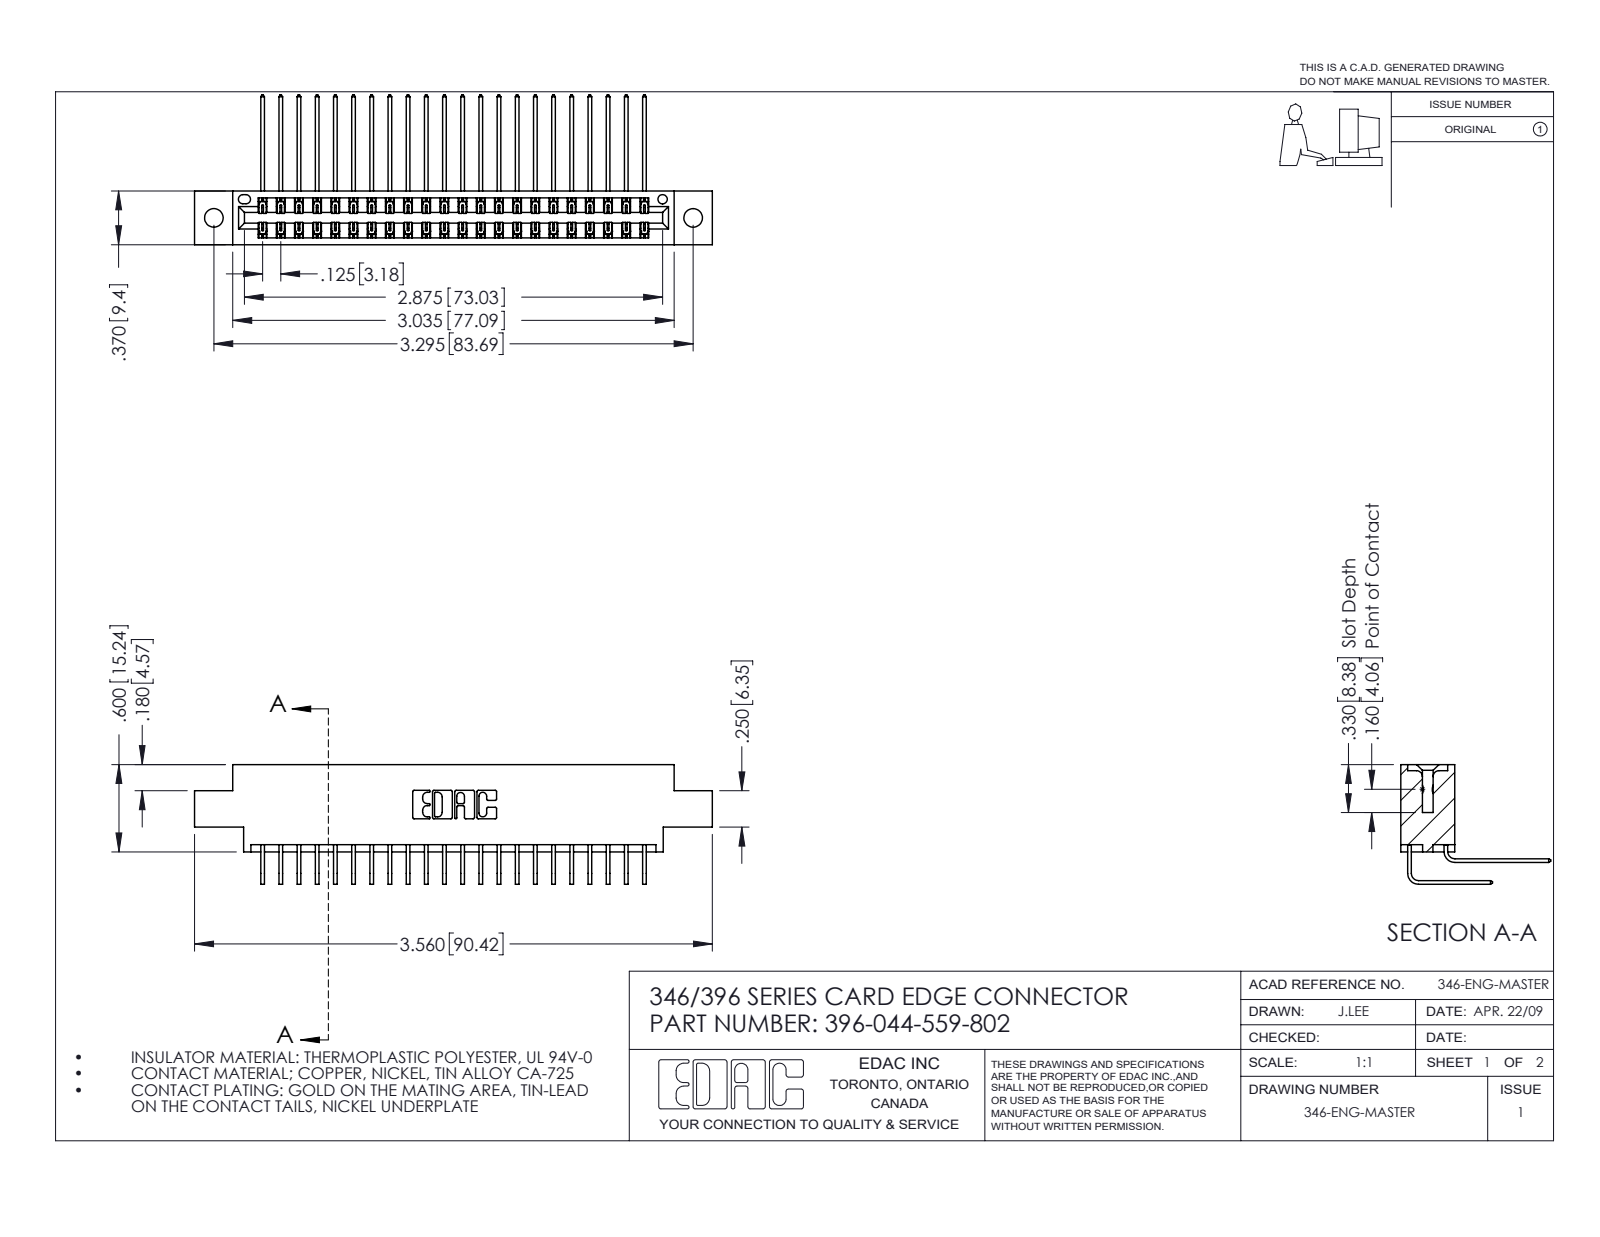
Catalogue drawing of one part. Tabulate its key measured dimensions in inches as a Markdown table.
| quantity | value |
| --- | --- |
| part name | 345-292-001_559 Tail - 2; 346 Part_0.170 Offset - 0.128 Dia; 345-292-001_558 559 Tail - 1; 396-044-559-802 |
| STEP written by | SolidWorks 2016 (CONFIG_CONTROL_DESIGN) |
| units | inches |
| bodies | 45 solids, 2502 faces (1708 planar, 794 cylindrical, 0 other) |
| overall size | 3.56 × 1.03 × 0.823 |
| volume | 0.532 in³ |
| surface area | 19.85 in² |
| round holes (diameter × count) | 0.128 × 2, 0.064 × 1 |
| partial cylindrical surfaces (radius × count) | 0.006 × 66, 0.01 × 22, 0.007 × 6, 0.031 × 6, 0.026 × 3, 0.014 × 2, 0.022 × 2, 0.024 × 2 |
| main face-to-face distances | 0.048, 0.322, 0.37, 0.025, 0.25, 0.072, 0.298, 0.275, 0.15, 0.148 |
| hole center spacings | 0.246, 3.087, 3.295 |
